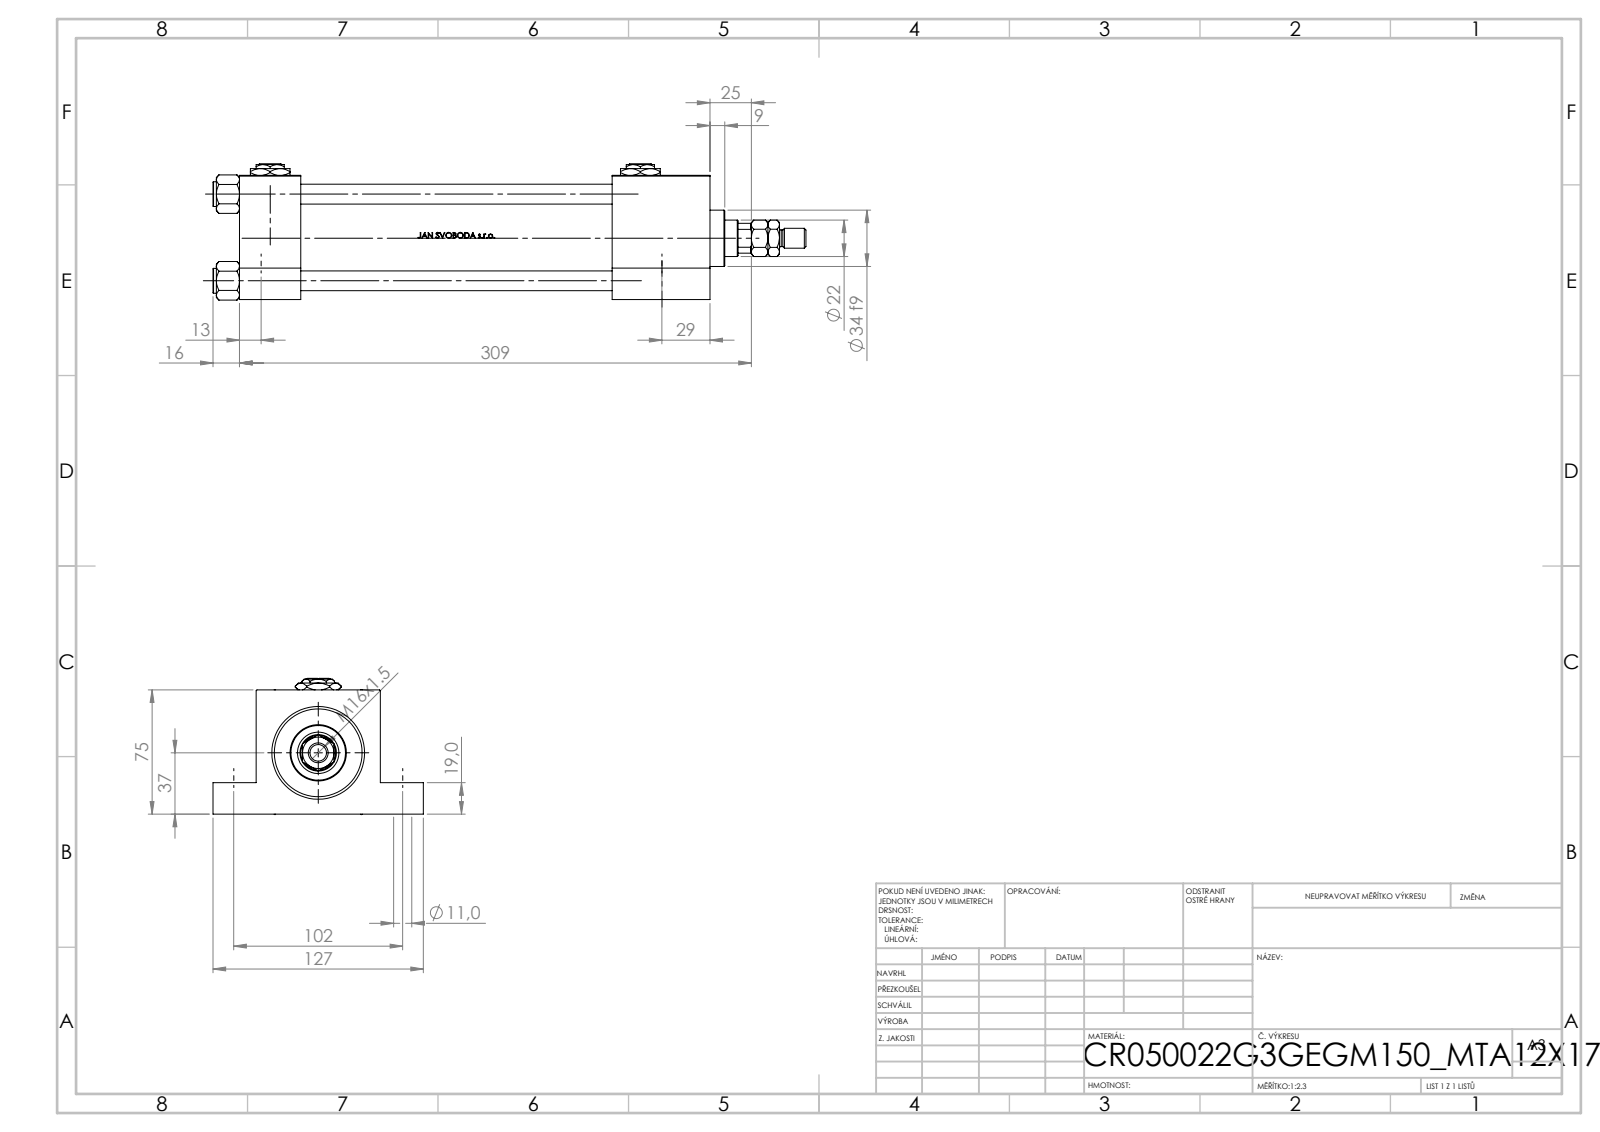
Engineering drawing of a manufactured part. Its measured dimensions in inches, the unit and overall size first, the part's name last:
Units: inches
Overall size (bounding box): 14.094 × 5 × 3.239
Round holes (diameter × count): ⌀0.472 ×4, ⌀0.551 ×4, ⌀0.276 ×2, ⌀0.825 ×2, ⌀1.181 ×2, ⌀0.413 ×1, ⌀0.866 ×1, ⌀0.984 ×1, ⌀1.614 ×1, ⌀1.969 ×1, ⌀2.087 ×1
Round bosses / shafts (diameter × count): ⌀0.591 ×4, ⌀2.205 ×1, ⌀1.339 ×1, ⌀0.472 ×1, ⌀0.394 ×1
Partial cylindrical surfaces — rounded edges, fillets, slot ends (radius × count): R0.413 ×1
Main face-to-face distances: 2.953, 1.457, 11.181, 9.724, 0.748, 8.858, 2.205, 7.402, 2.323, 3.976
Hole centre spacings: 1.456, 2.059, 2.02, 2.072, 2.912, 4.016, 9.237, 9.525
Volume: 61.08 in³ · Surface area: 403.6 in²
Bodies: 18 solids, 1301 faces (511 planar, 140 cylindrical, 650 other)
Part name (STEP PRODUCT): V215CR_G_Body; V215_VC_A; NUT_M5_G; V215CR_VCP_G (+3 more)
STEP written by: SolidWorks 2019 (CONFIG_CONTROL_DESIGN)
